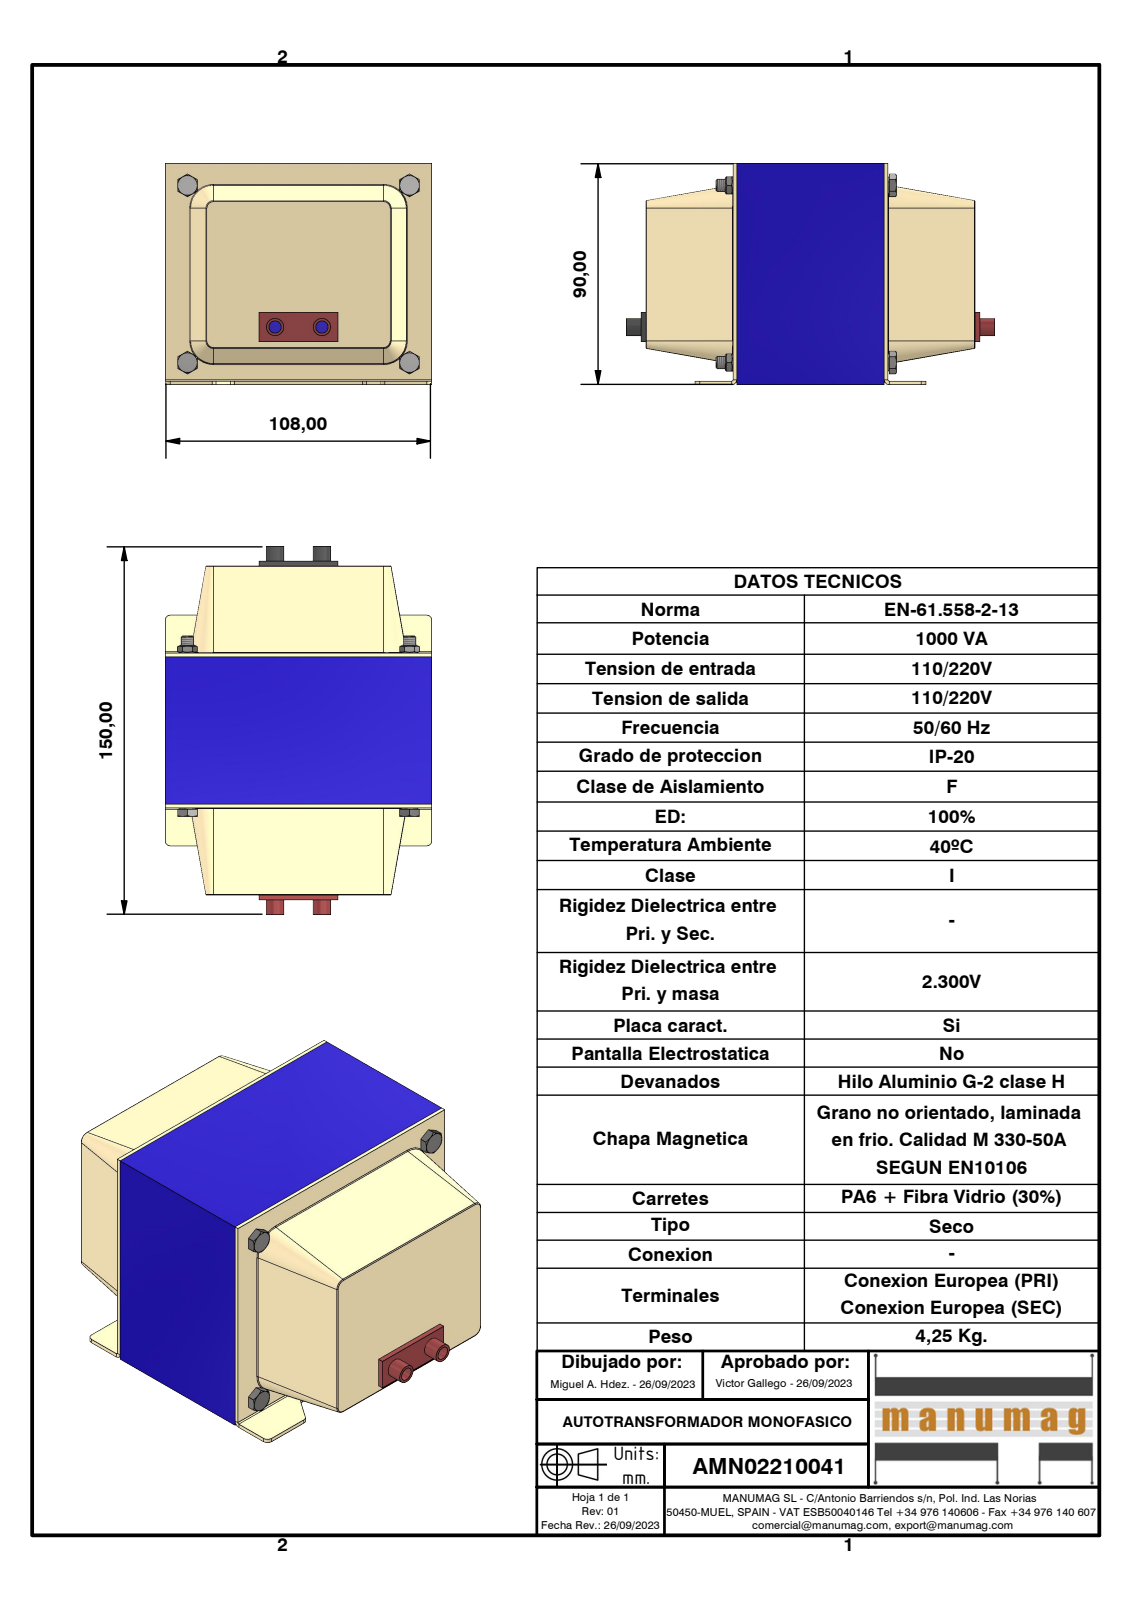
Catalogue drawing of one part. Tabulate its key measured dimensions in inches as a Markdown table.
| quantity | value |
| --- | --- |
| part name | AMN002210041; EI108 x 90 - 60 (RC36) Azul; TAPA RC36 RECEPTACULO; Receptaculo negro (+3 more) |
| STEP written by | Autodesk Inventor 2023 (AUTOMOTIVE_DESIGN) |
| units | inches |
| bodies | 13 solids, 310 faces (162 planar, 68 cylindrical, 80 other) |
| overall size | 5.906 × 4.252 × 3.543 |
| volume | 30.5 in³ |
| surface area | 225.9 in² |
| round holes (diameter × count) | 0.197 × 6, 0.128 × 4, 0.22 × 4 |
| round bosses / shafts (diameter × count) | 0.264 × 4, 0.18 × 4, 0.276 × 2 |
| partial cylindrical surfaces (radius × count) | 0.015 × 16, 0.079 × 14, 0.02 × 2 |
| main face-to-face distances | 0.709, 0.059, 3.819, 1.398, 2.835, 3.543, 2.362, 1.417, 3.235, 1.457 |
| hole center spacings | 1.509, 2.22, 2.662, 2.835, 3.12, 3.543, 4.538, 0.748 |
